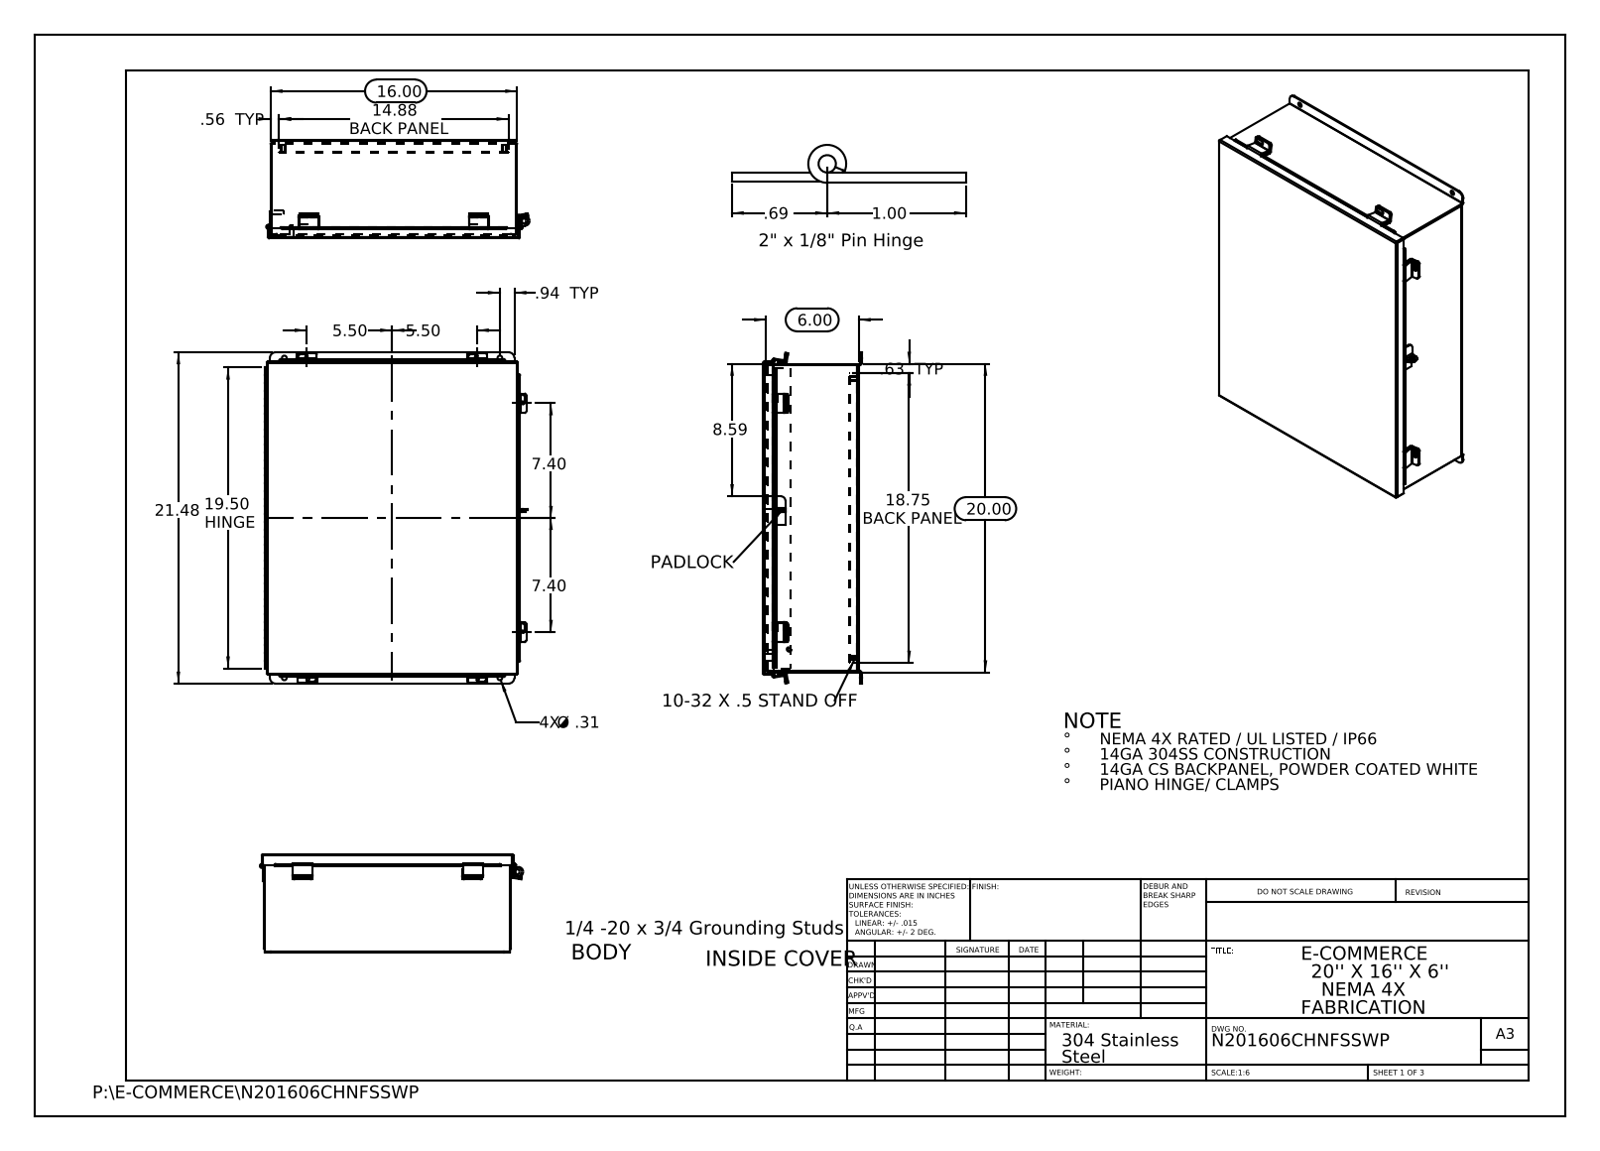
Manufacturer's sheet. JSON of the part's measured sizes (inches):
{"part_name": "N201606CHNFSSWP Hinge Body Side; N201606CHNFSSWP JIC_Standoff; N201606CHNFSSWP JIC Top; N201606CHNFSSWP JIC Clamp Bracket (+8 more)", "step_written_by": "SolidWorks 2013 (CONFIG_CONTROL_DESIGN)", "units": "inches", "bodies": {"solids": 27, "faces": 938, "planar": 579, "cylindrical": 339, "other": 20}, "overall_size": [21.476, 17.072, 6.39], "volume_in3": 113, "surface_area_in2": 3067, "round_holes": [[0.25, 10], [0.187, 4], [0.312, 4], [0.125, 1], [0.125, 1], [0.373, 1], [0.375, 1]], "round_bosses_or_shafts": [[0.313, 4], [0.315, 2], [0.236, 2], [0.273, 1], [0.25, 1]], "partial_cylinders_radius": [[0.125, 21], [0.013, 13], [0.009, 12], [0.088, 12], [0.133, 12], [0.083, 6], [0.1, 6], [0.375, 4]], "face_to_face_distances": [0.075, 6.128, 6.053, 6.203, 0.074, 5.628, 0.575, 0.5, 5.553, 0.649], "hole_center_spacings": [1.315, 14.235, 19.427, 24.048, 11, 13.976, 14.375, 18.126]}
